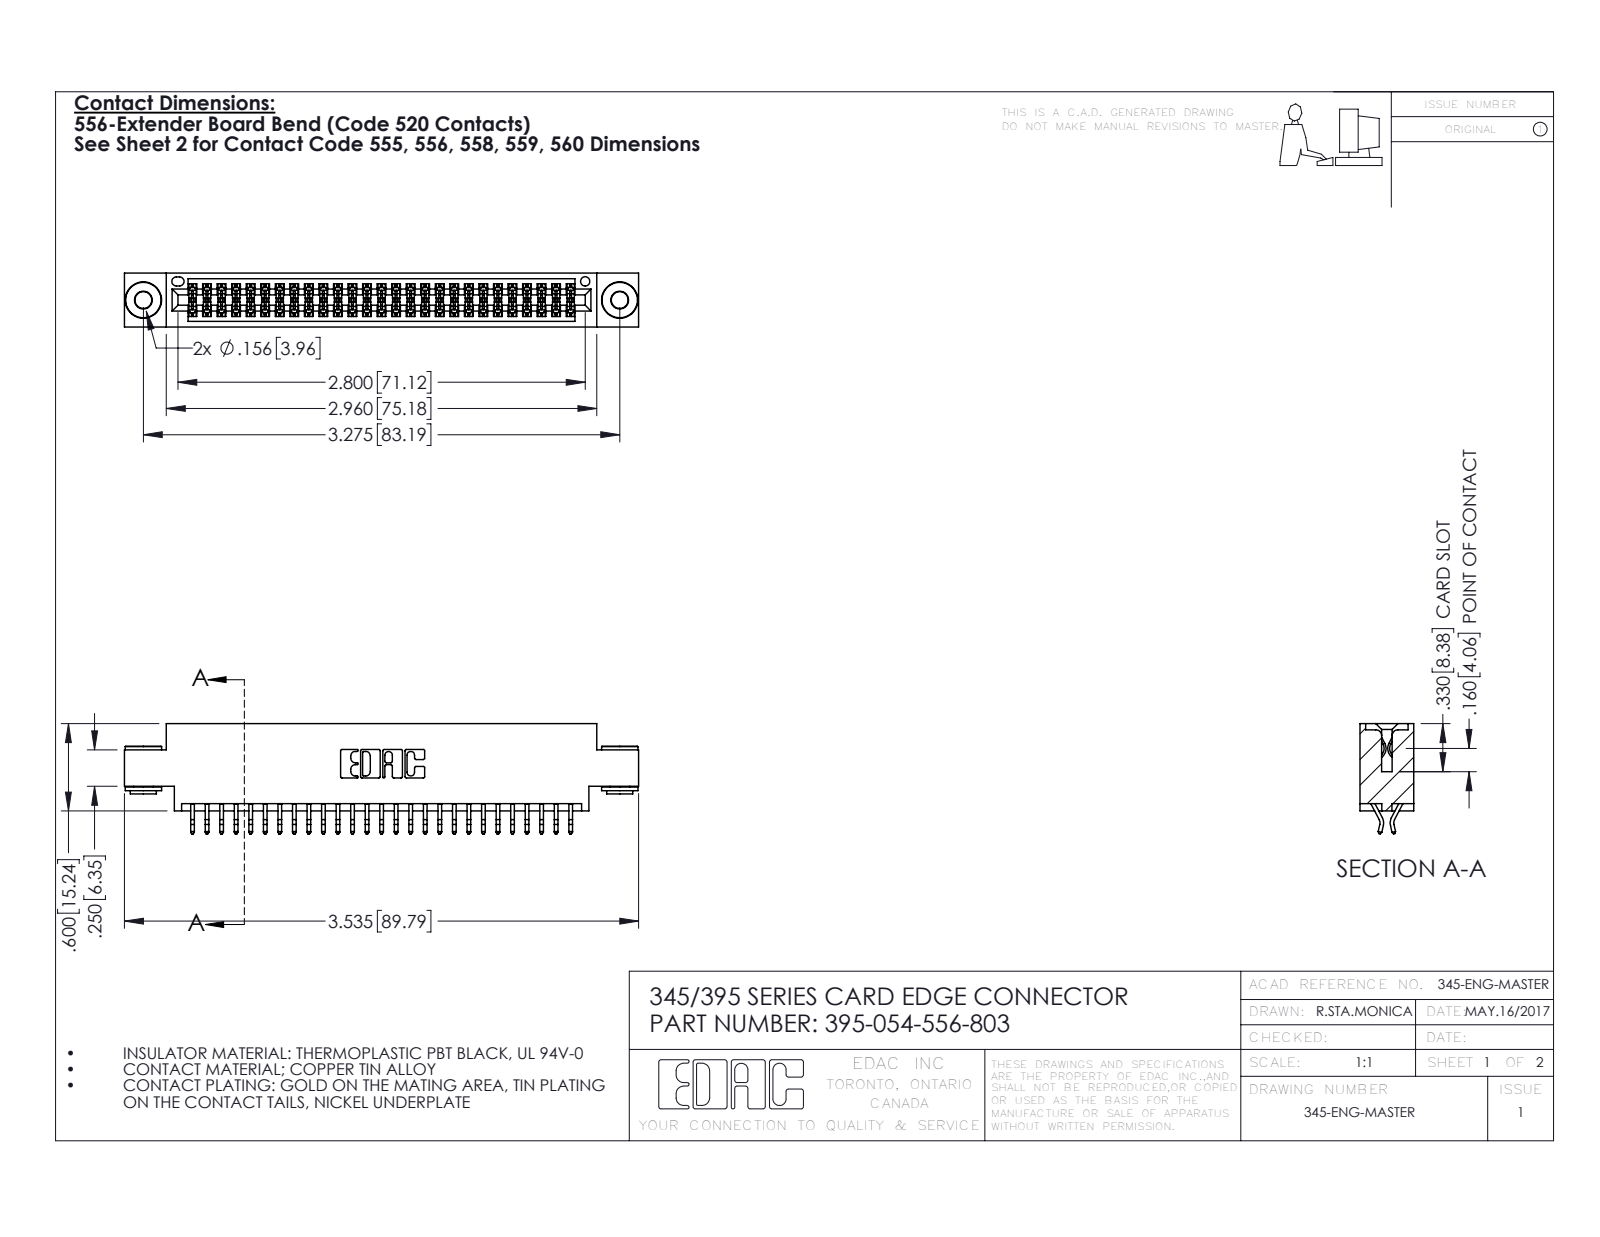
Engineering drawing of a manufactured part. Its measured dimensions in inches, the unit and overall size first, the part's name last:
Units: inches
Overall size (bounding box): 3.535 × 0.757 × 0.37
Round holes (diameter × count): ⌀0.116 ×2, ⌀0.156 ×2, ⌀0.064 ×1
Round bosses / shafts (diameter × count): ⌀0.25 ×2, ⌀0.18 ×2, ⌀0.136 ×2
Partial cylindrical surfaces — rounded edges, fillets, slot ends (radius × count): R0.006 ×81, R0.01 ×22, R0.007 ×6, R0.031 ×6, R0.026 ×3, R0.01 ×2, R0.014 ×2, R0.019 ×2
Main face-to-face distances: 0.072, 0.298, 0.37, 0.2, 0.025, 0.098, 0.272, 0.225, 0.175, 0.1
Hole centre spacings: 0.27, 3.04, 3.275
Volume: 0.518 in³ · Surface area: 19.46 in²
Bodies: 57 solids, 3192 faces (2092 planar, 1092 cylindrical, 8 other)
Part name (STEP PRODUCT): 395-054-556-803; 345-250-002_345-250-002-102; 345-292-001_556 Tail; 345 Part_0.170 Offset - 0.156 Dia-TH
STEP written by: SolidWorks 2016 (CONFIG_CONTROL_DESIGN)
